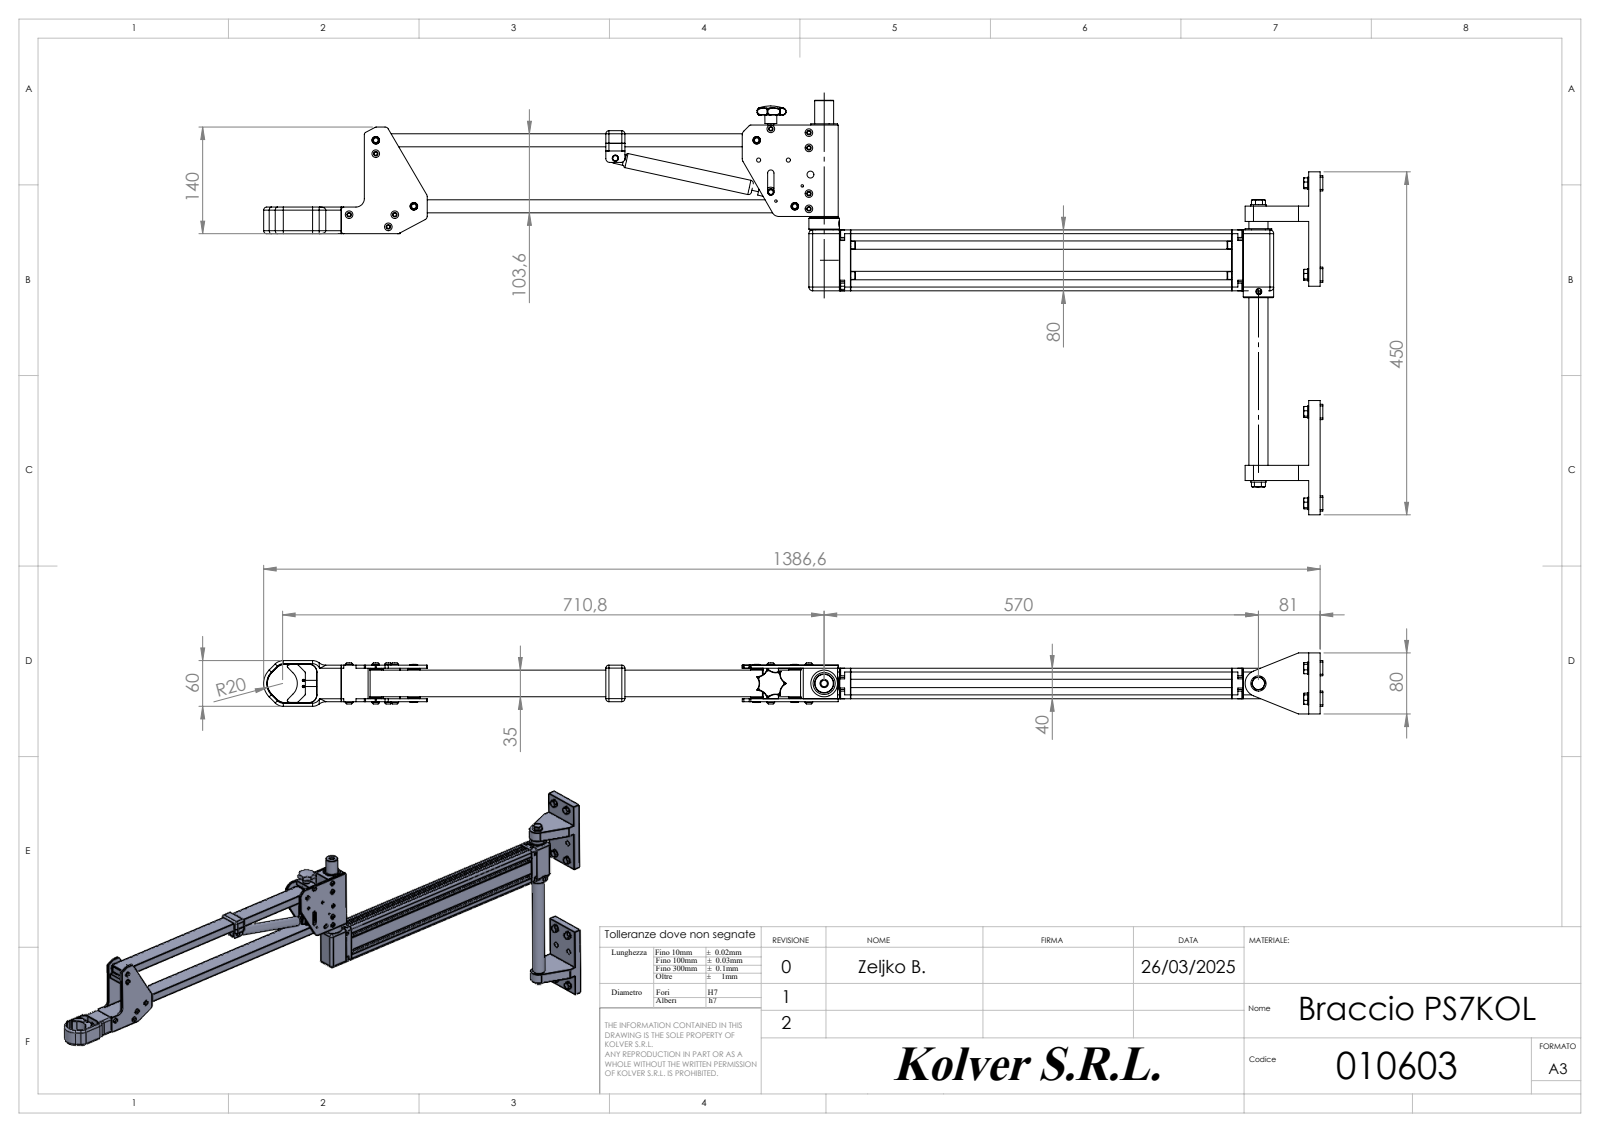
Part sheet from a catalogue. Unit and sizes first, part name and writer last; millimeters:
Units: millimetres
Overall size (bounding box): 1390.14 × 450 × 80
Round holes (diameter × count): ⌀20.5 ×8, ⌀11 ×4, ⌀3 ×2, ⌀3.24 ×2, ⌀5.5 ×2, ⌀6.5 ×2, ⌀6.65 ×2, ⌀5.3 ×1, ⌀6 ×1, ⌀8 ×1, ⌀8.02 ×1, ⌀8.38 ×1
Round bosses / shafts (diameter × count): ⌀10 ×20, ⌀16 ×12, ⌀19.22 ×4, ⌀8 ×4, ⌀15 ×3, ⌀40 ×2, ⌀35 ×2, ⌀14 ×2
Partial cylindrical surfaces — rounded edges, fillets, slot ends (radius × count): R2 ×44, R4 ×20, R5 ×14, R13.33 ×7, R3 ×5, R14 ×4, R15 ×4, R7 ×3
Main face-to-face distances: 40, 4, 44, 37.5, 86.6, 17, 2.5, 6.5, 41.5, 11.4
Hole centre spacings: 40, 56.57, 300, 302.65, 79.07, 93.27, 103.06, 115.25
Bodies: 0 solids, 1100 faces (633 planar, 281 cylindrical, 186 other)
Part name (STEP PRODUCT): PS7KOL
STEP written by: SolidWorks 2024 (AUTOMOTIVE_DESIGN)
